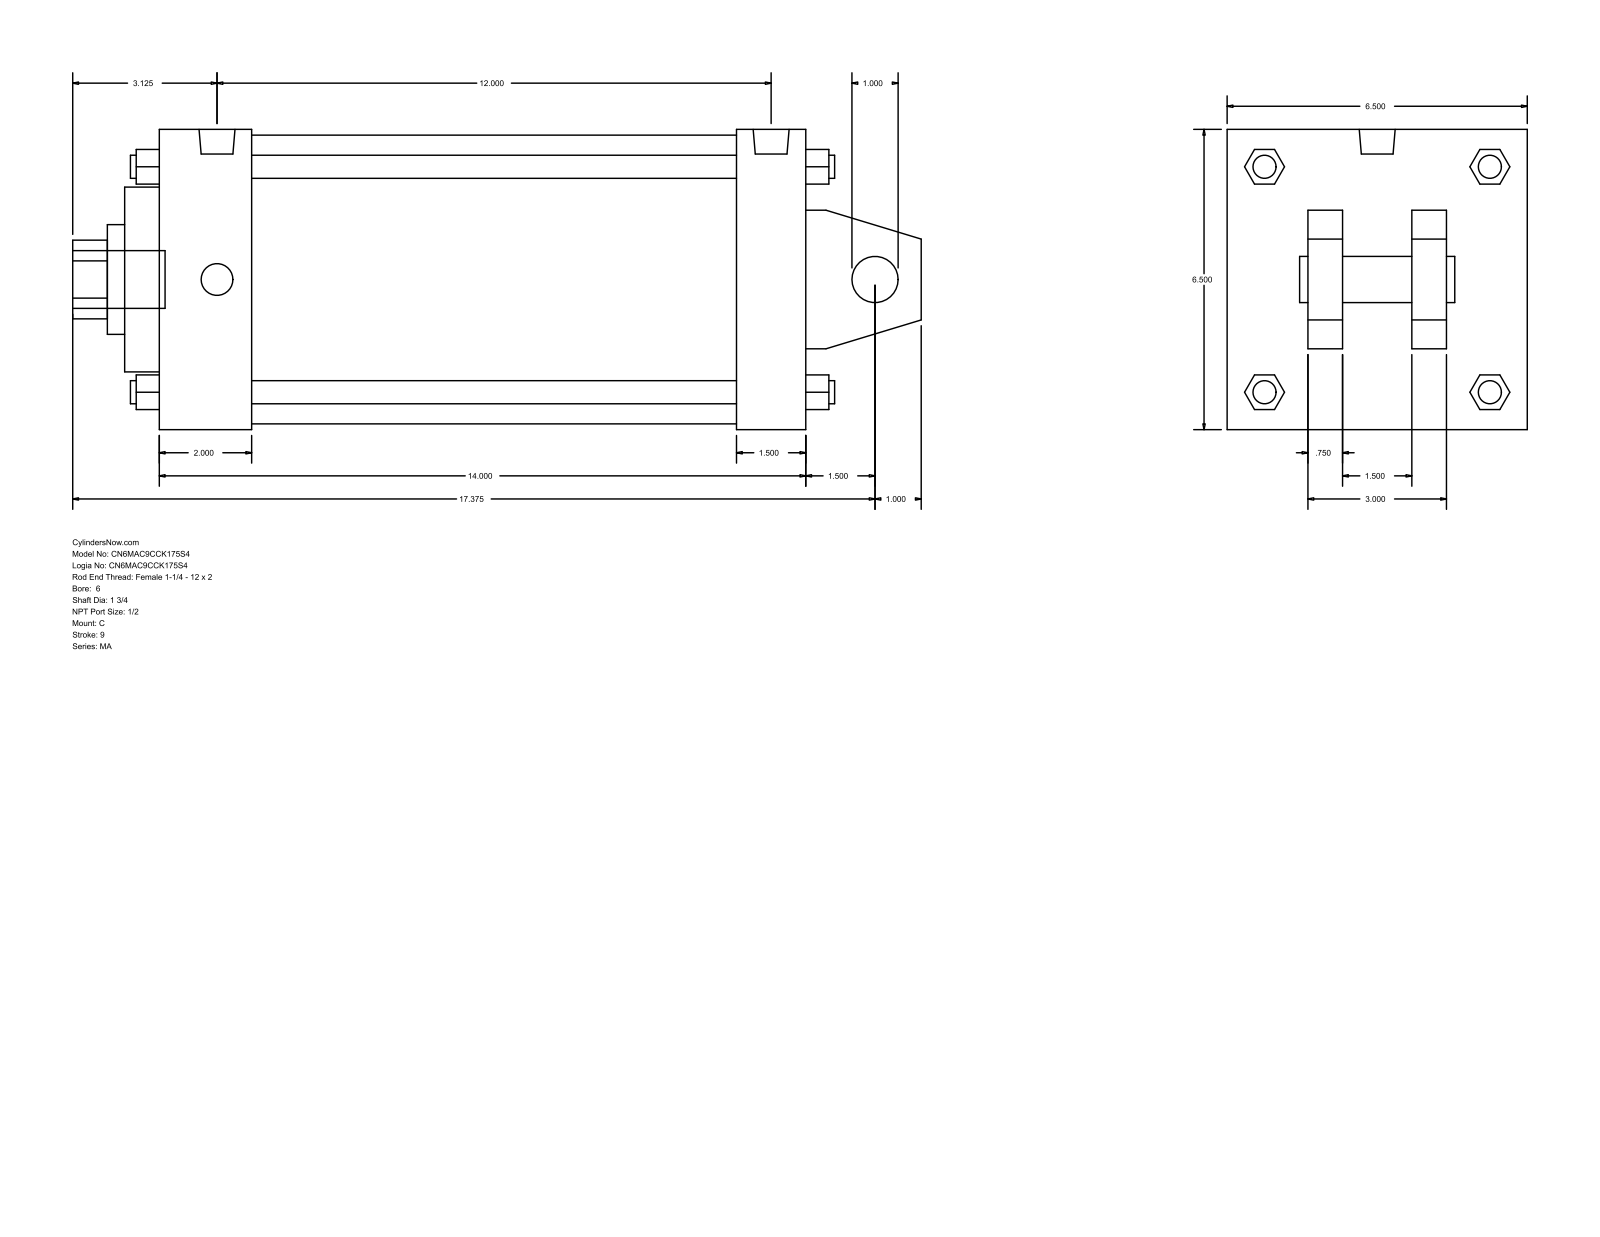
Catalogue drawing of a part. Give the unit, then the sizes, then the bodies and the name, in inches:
Units: inches
Overall size (bounding box): 18.375 × 6.5 × 6.5
Round holes (diameter × count): ⌀1 ×1, ⌀1.75 ×1, ⌀2.375 ×1, ⌀4 ×1, ⌀6.25 ×1
Round bosses / shafts (diameter × count): ⌀0.687 ×4, ⌀0.5 ×4, ⌀0.778 ×2, ⌀1.25 ×1
Partial cylindrical surfaces — rounded edges, fillets, slot ends (radius × count): R0.852 ×1
Main face-to-face distances: 6.5, 14, 0.75, 2.5, 4, 2, 1.75, 4.75, 2.25, 12
Bodies: 0 solids, 141 faces (109 planar, 32 cylindrical, 0 other)
Part name (STEP PRODUCT): MA_C__0600_1.75
STEP written by: GSSL Pune (CONFIG_CONTROL_DESIGN)
